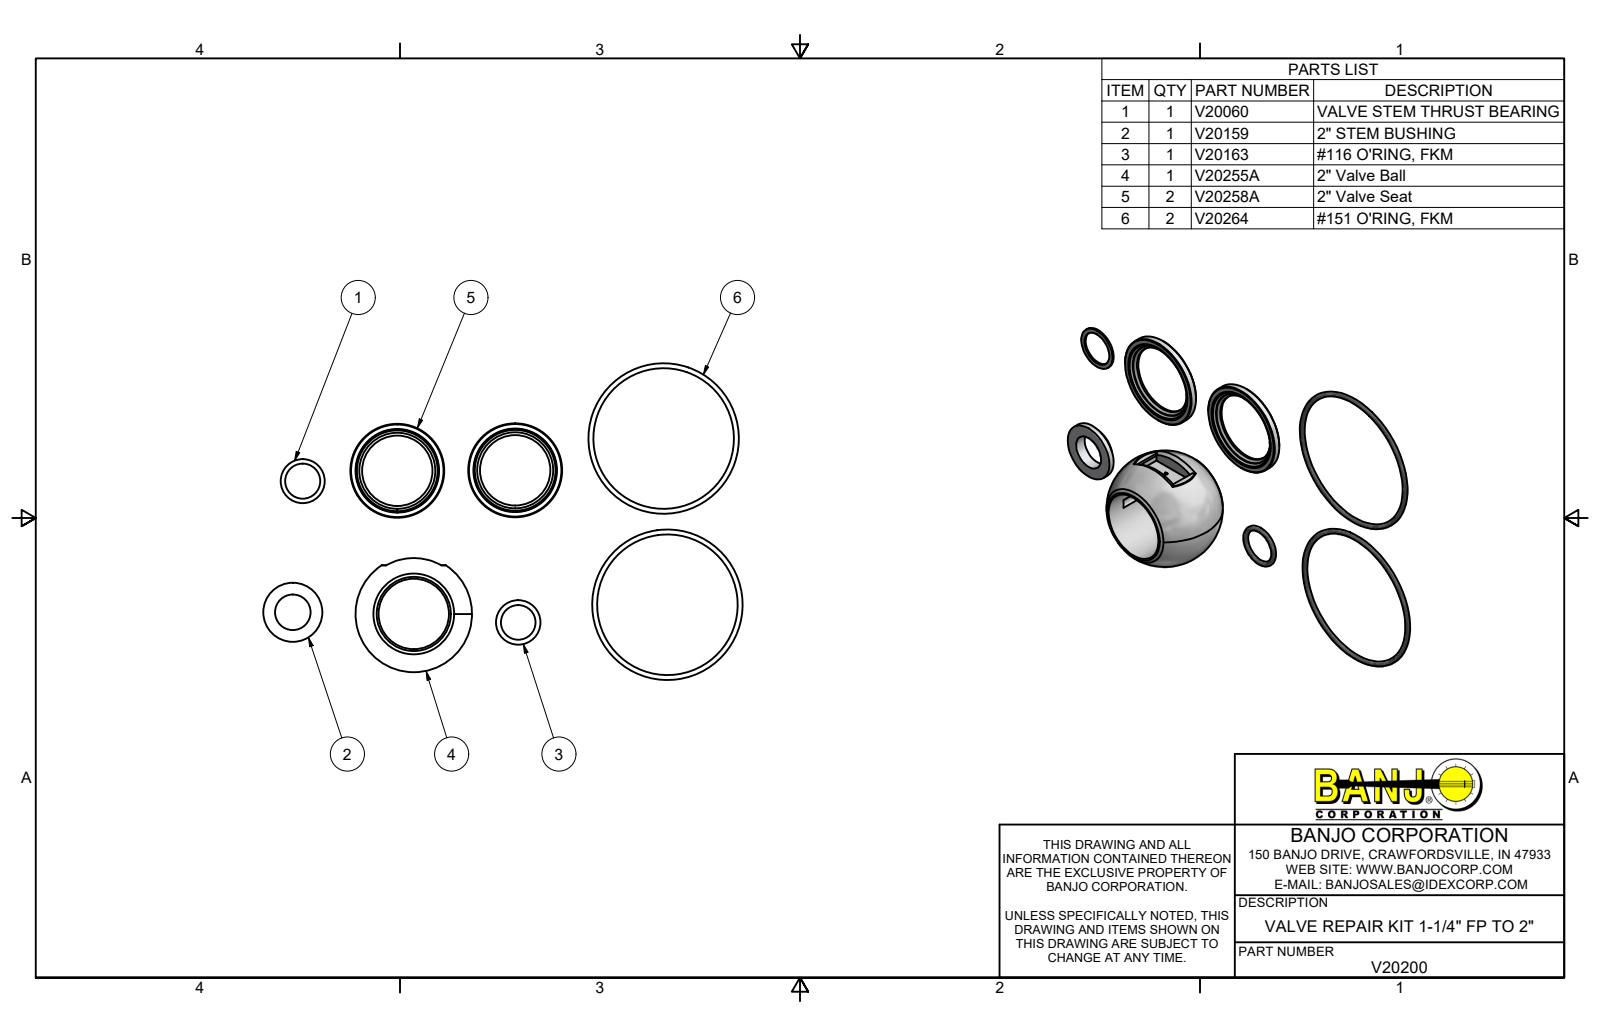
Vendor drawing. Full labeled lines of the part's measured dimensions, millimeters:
Part name (STEP PRODUCT): V20200; V20060; V20159; V20163 (+5 more)
STEP written by: Autodesk Inventor 2019 (AUTOMOTIVE_DESIGN)
Units: millimetres
Bodies: 8 solids, 85 faces (38 planar, 17 cylindrical, 30 other)
Overall size (bounding box): 258.6 × 170.7 × 47.5
Volume: 73 770 mm³ · Surface area: 28 340 mm²
Round holes (diameter × count): ⌀38.1 ×3, ⌀39.8 ×2, ⌀41 ×2, ⌀19.1 ×1, ⌀19.1 ×1
Round bosses / shafts (diameter × count): ⌀50.8 ×2, ⌀44.9 ×2, ⌀31.9 ×1, ⌀23.8 ×1, ⌀23.5 ×1
Partial cylindrical surfaces — rounded edges, fillets, slot ends (radius × count): R3.2 ×1
Main face-to-face distances: 0.3, 4.5, 4.2, 0.9, 0.6, 3.6, 2.2, 2.5, 3.2, 6.7
Hole centre spacings: 51.3, 63.6, 65.3, 70.9, 77.8, 93.4, 94.9, 94.9
